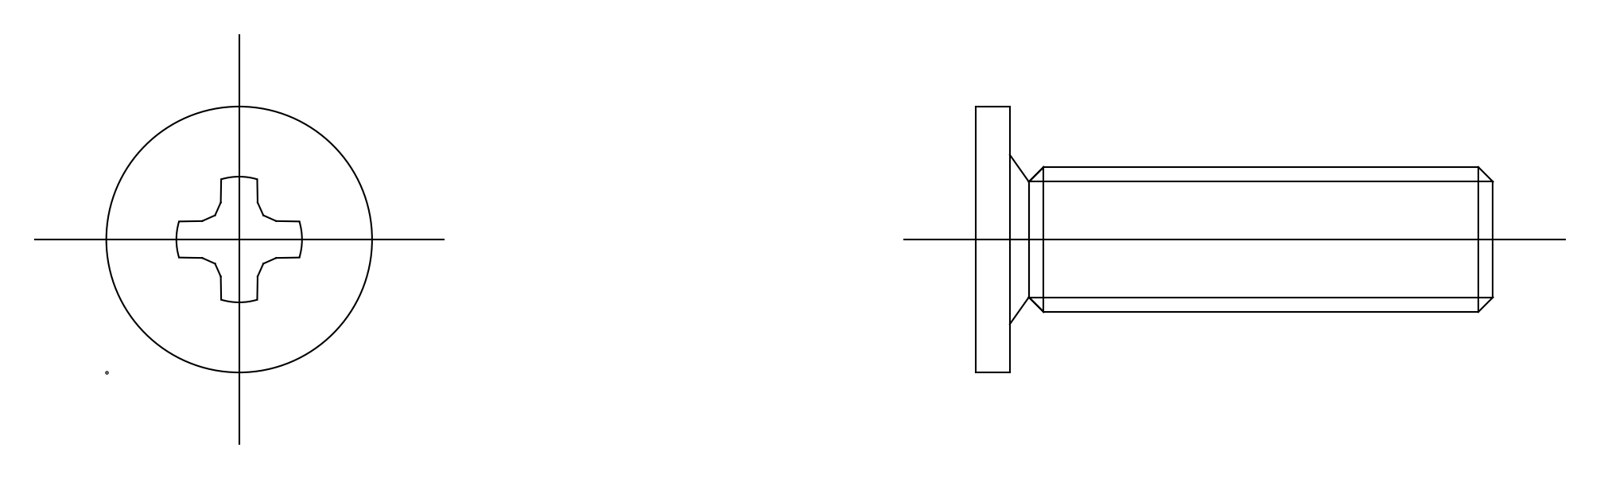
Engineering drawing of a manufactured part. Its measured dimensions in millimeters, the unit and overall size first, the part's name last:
Units: millimetres
Overall size (bounding box): 10.7 × 5.5 × 5.5
Round bosses / shafts (diameter × count): ⌀5.5 ×1, ⌀3 ×1
Main face-to-face distances: 0.7, 10.7, 10, 1.32, 0.78
Volume: 84 mm³ · Surface area: 160 mm²
Bodies: 1 solid, 29 faces (19 planar, 4 cylindrical, 6 other)
STEP written by: spGate 20.6.3 (****-****-****-****) (AUTOMOTIVE_DESIGN)
